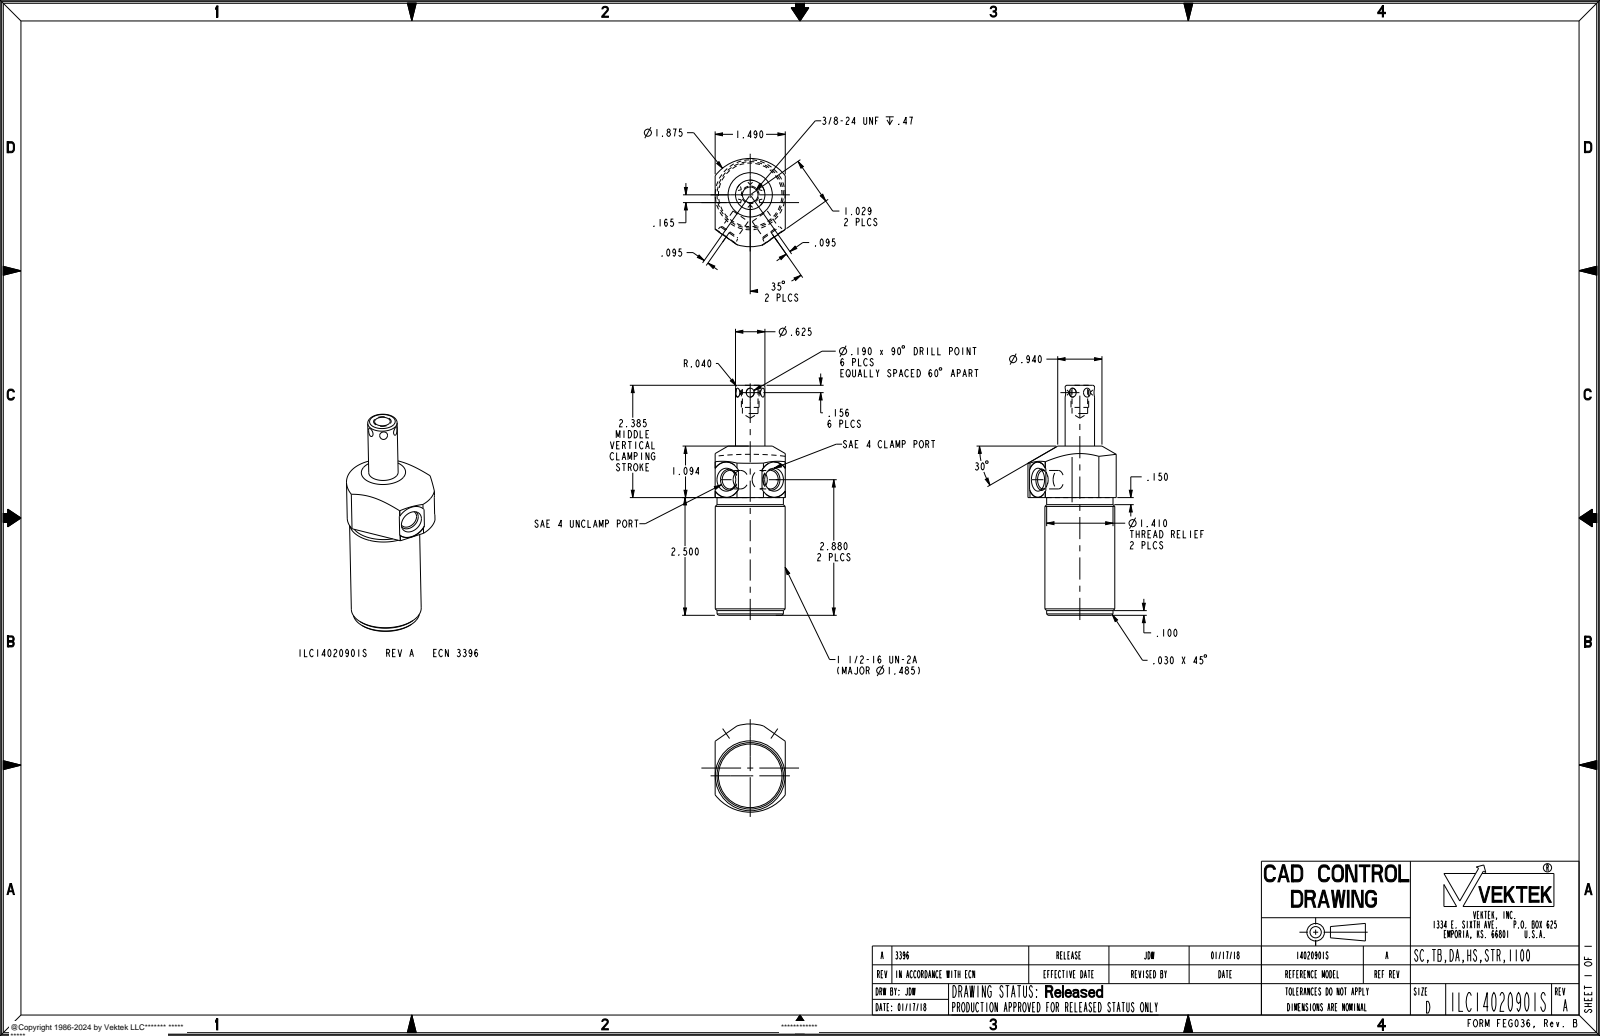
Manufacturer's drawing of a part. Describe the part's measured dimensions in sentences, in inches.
The part is named "ILC14020901S". Its 3-D file was written by "PRO/ENGINEER BY PARAMETRIC TECHNOLOGY CORPORATION, 2013320 (AUTOMOTIVE_DESIGN)". It is 1 solid with 73 faces: 15 planar, 26 cylindrical and 32 other. Overall it measures 4.885 by 1.875 by 1.49 inches. Its volume is 6.874 cubic inches and its surface area 26.7 square inches. Round holes: 2 of diameter 0.392, 1 of diameter 0.332. Round bosses or shafts: 1 of diameter 1.485, 1 of diameter 1.41, 1 of diameter 0.625, 1 of diameter 0.375. Partial cylindrical surfaces (rounded edges, fillets, slot ends): 2 of radius 0.375, 1 of radius 0.937. The main face-to-face distances are 1.49, 2.5, 3.594, 1.094, 0.53, 4.885, 2.385, 1.291, 0.54, 0.54.
